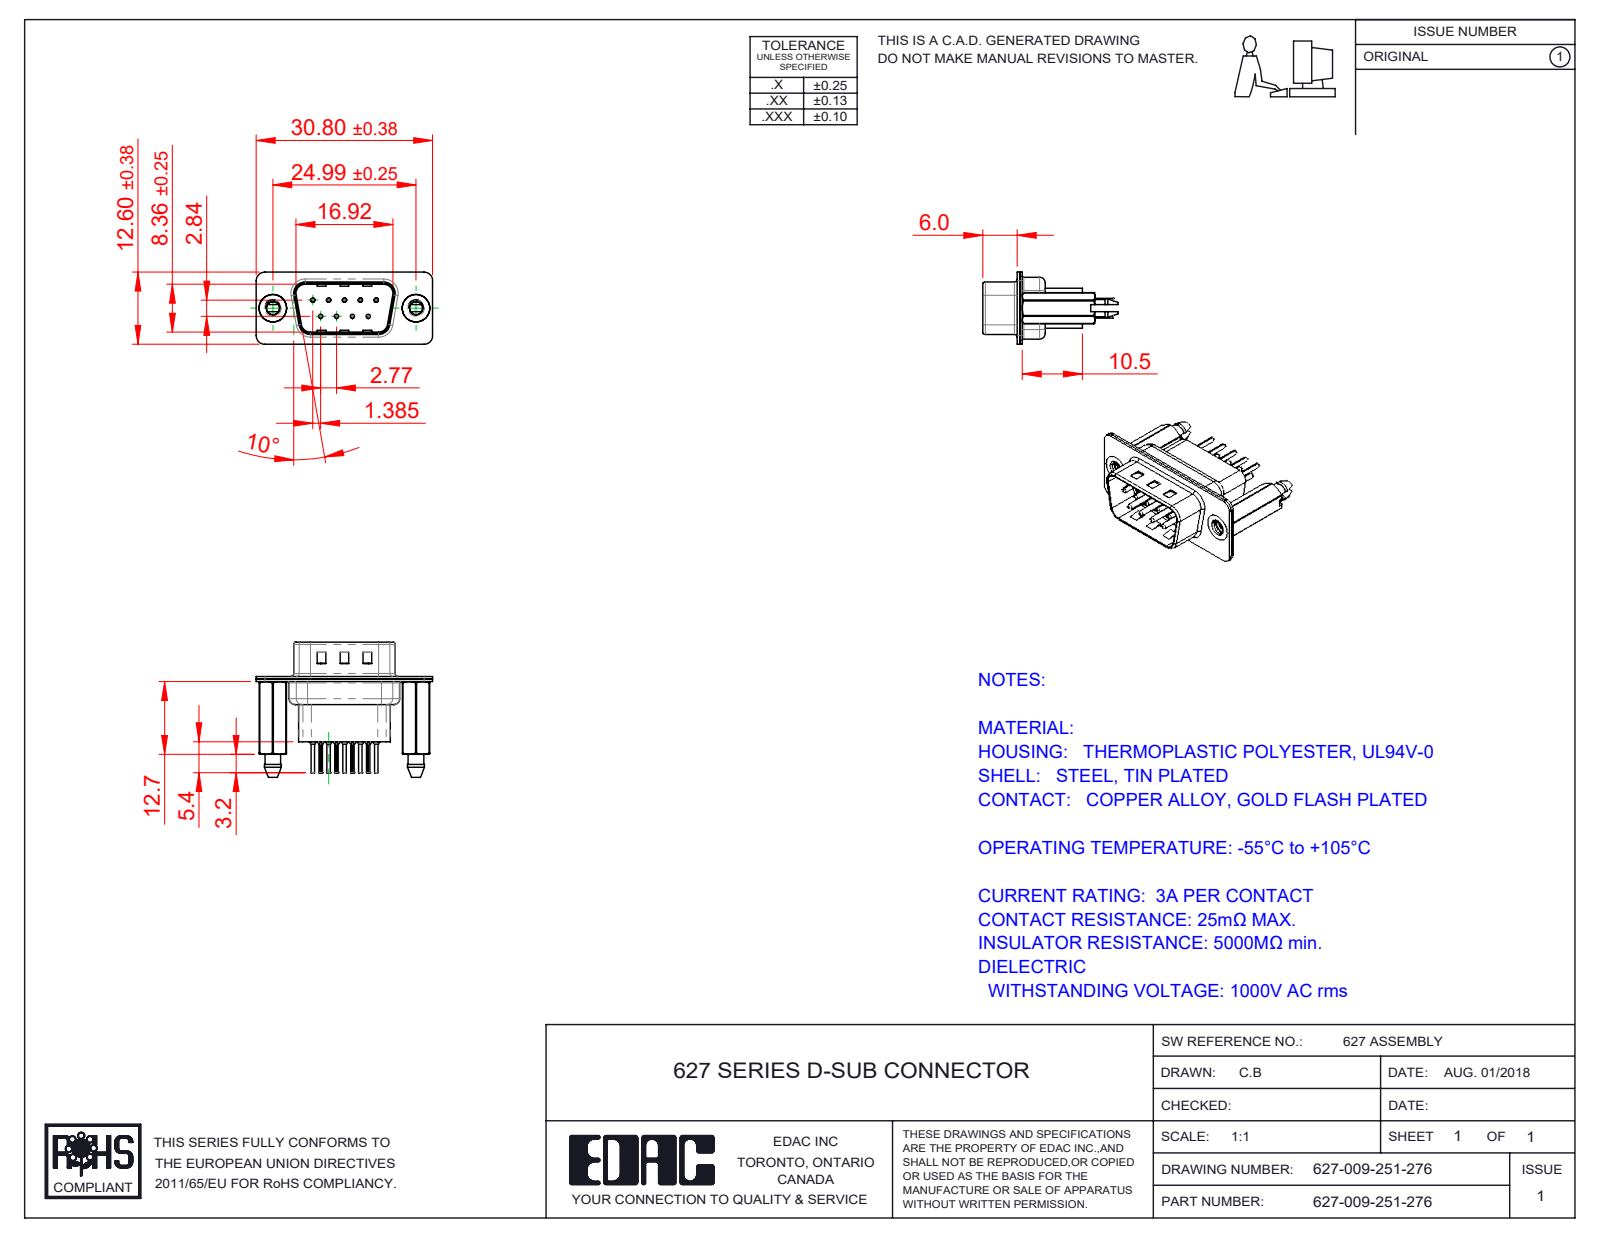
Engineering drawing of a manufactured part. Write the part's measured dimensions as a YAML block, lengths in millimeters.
part_name: "627 Shell Front_09 Contacts; 627 Contact Row 1_41; 627 Contact Row 2_41; 627-009-251-076 (+3 more)"
step_written_by: "SolidWorks 2020 (CONFIG_CONTROL_DESIGN)"
units: millimeters
bodies: {solids: 14, faces: 1294, planar: 355, cylindrical: 528, other: 411}
overall_size: [30.8, 23.6, 12.6]
volume: 2087
surface_area: 5423
round_holes:
  - {diameter: 0.2, count: 9}
  - {diameter: 0.35, count: 9}
  - {diameter: 1.1, count: 9}
  - {diameter: 1.6, count: 9}
  - {diameter: 2.26, count: 2}
  - {diameter: 4, count: 2}
  - {diameter: 4.8, count: 2}
round_bosses_or_shafts:
  - {diameter: 2, count: 9}
  - {diameter: 1.5, count: 9}
  - {diameter: 0.75, count: 9}
  - {diameter: 0.6, count: 9}
  - {diameter: 4.9, count: 2}
partial_cylinders:
  - {radius: 1.5, count: 20}
  - {radius: 0.1, count: 18}
  - {radius: 2, count: 12}
  - {radius: 1.6, count: 10}
  - {radius: 0.5, count: 8}
  - {radius: 0.25, count: 4}
  - {radius: 0.6, count: 4}
  - {radius: 0.65, count: 4}
face_to_face_distances: [0.45, 0.4, 0.9, 0.82, 9.58, 1.4, 1.5, 4.76, 0.68, 7.68]
hole_center_spacings: [3.16, 2.77, 5.54, 5.03, 5.04, 8.31, 7.48, 7.49]
